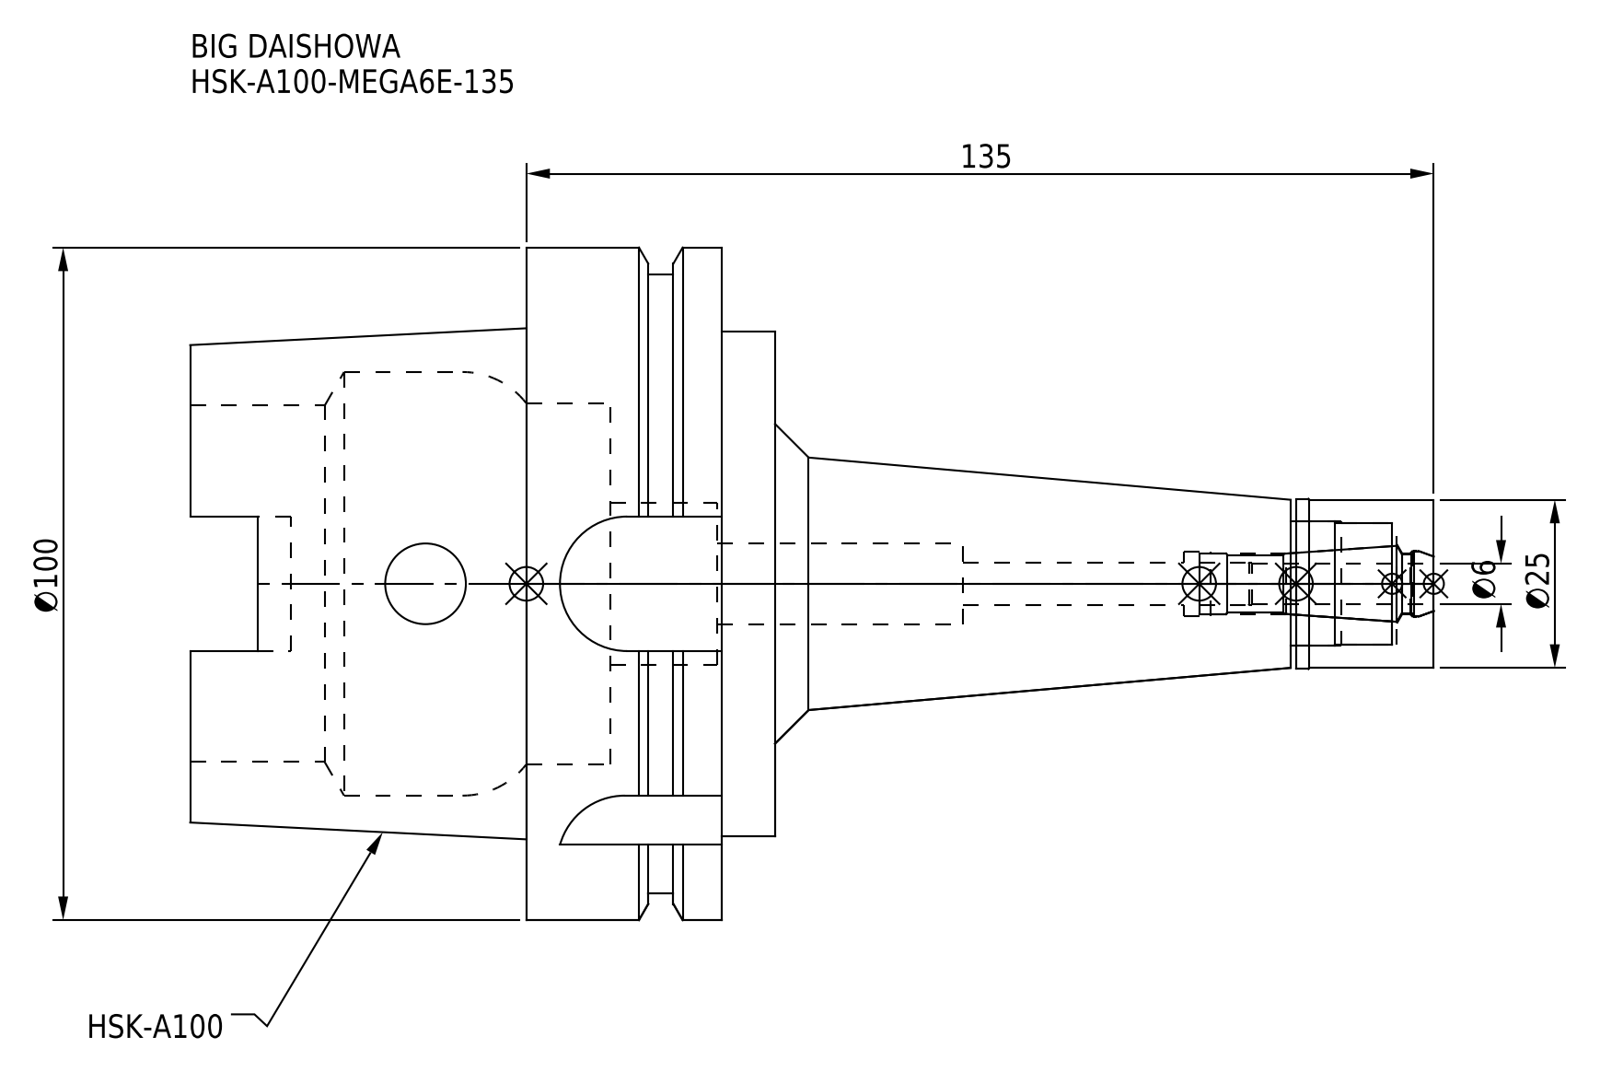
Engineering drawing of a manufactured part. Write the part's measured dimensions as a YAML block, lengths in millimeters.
part_name: "HSK-A100-MEGA6E-135-060-FreeParts; HSK-A100-MEGA6E-135-060.stp; HSK-A100-MEGA6E-135_1.stp; MEN6_1.stp (+3 more)"
step_written_by: "SolidWorks 2019 (CONFIG_CONTROL_DESIGN)"
units: millimeters
bodies: {solids: 2, faces: 126, planar: 42, cylindrical: 56, other: 28}
overall_size: [185, 100, 100]
volume: 354183
surface_area: 65882
round_holes:
  - {diameter: 12, count: 2}
  - {diameter: 6.4, count: 1}
  - {diameter: 9, count: 1}
  - {diameter: 9.6, count: 1}
  - {diameter: 9.9, count: 1}
  - {diameter: 18, count: 1}
  - {diameter: 18.5, count: 1}
  - {diameter: 24, count: 1}
  - {diameter: 53, count: 1}
  - {diameter: 53.8, count: 1}
  - {diameter: 63, count: 1}
round_bosses_or_shafts:
  - {diameter: 100, count: 1}
  - {diameter: 92, count: 1}
  - {diameter: 75, count: 1}
  - {diameter: 25.3, count: 1}
  - {diameter: 25, count: 1}
partial_cylinders:
  - {radius: 4.88, count: 4}
  - {radius: 10, count: 4}
face_to_face_distances: [29, 8, 37, 24.55, 16.55, 12.45, 87, 79, 62.45, 50]
